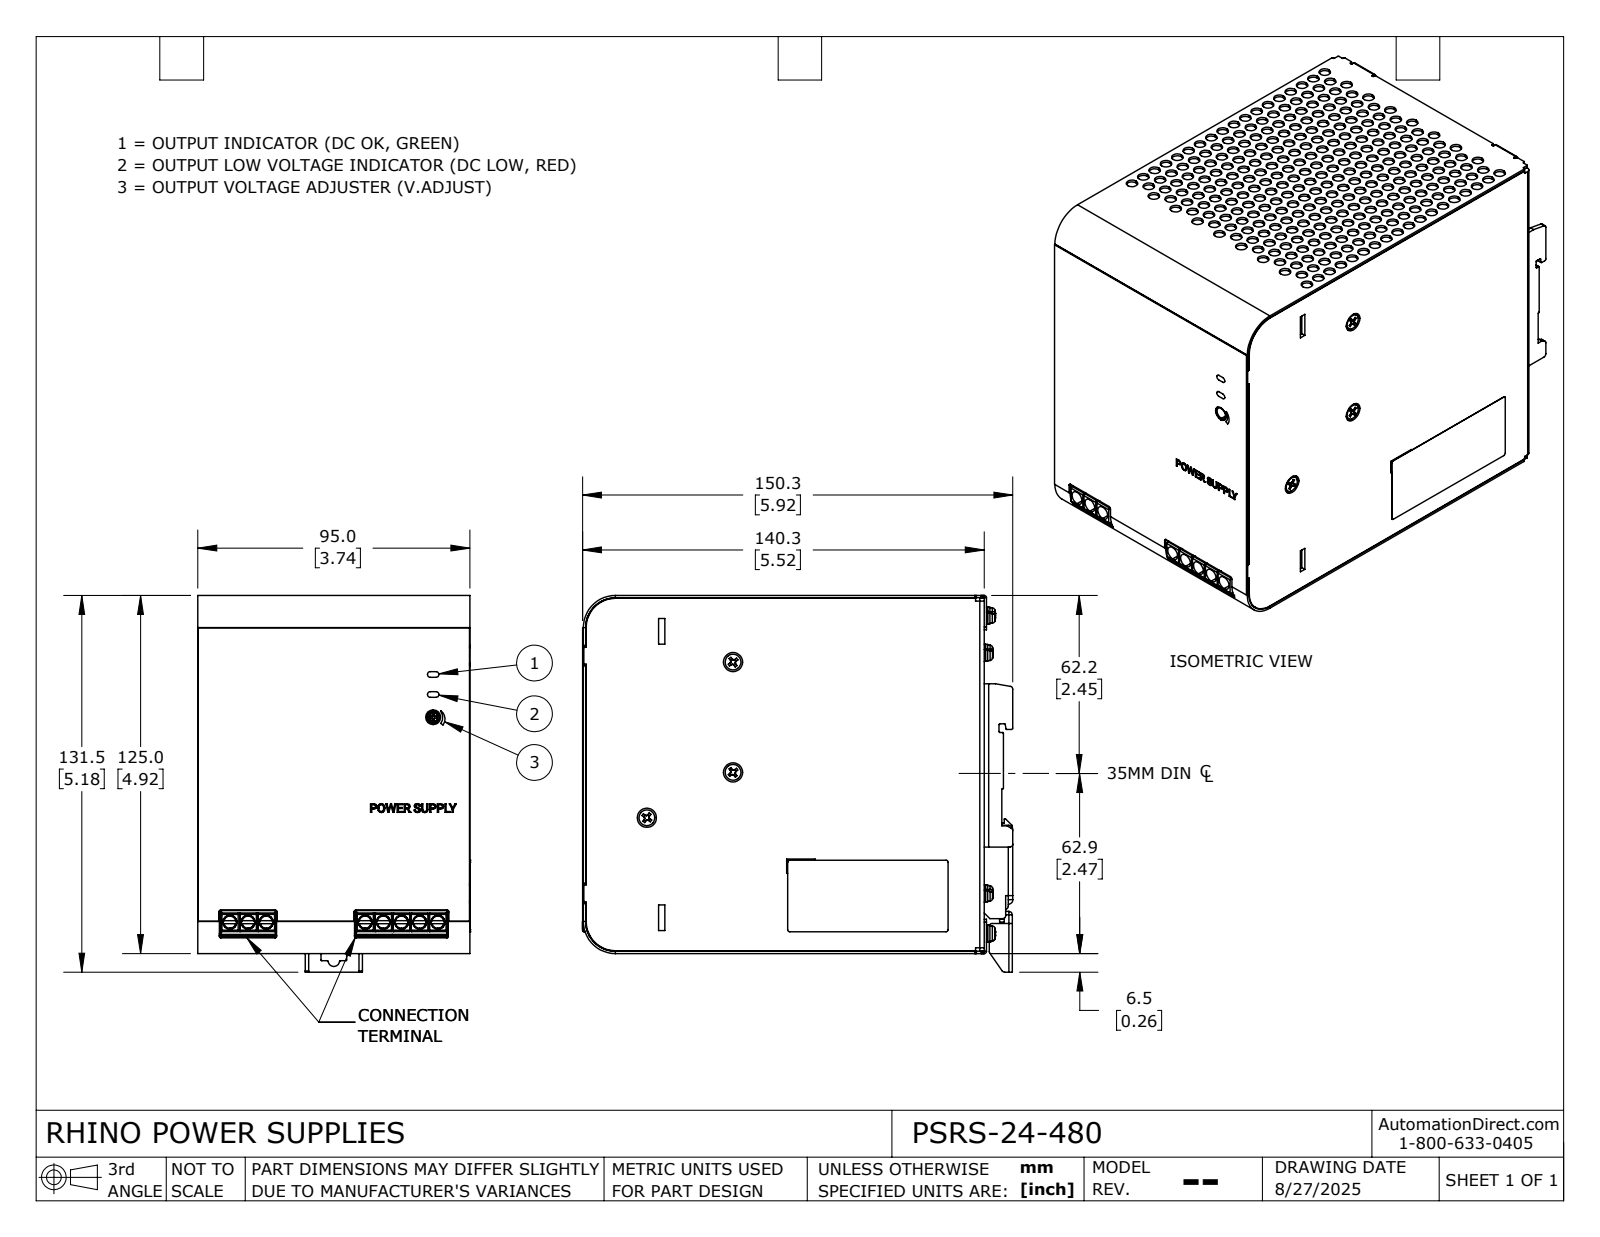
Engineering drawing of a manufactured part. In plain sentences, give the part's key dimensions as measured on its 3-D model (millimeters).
The part is named "PSRS-24-480". Its 3-D file was written by "SolidWorks 2024 (AUTOMOTIVE_DESIGN)". It is 4 solids with 4312 faces: 1983 planar, 1867 cylindrical and 462 other. Overall it measures 150.25 by 131.5 by 95.05 millimeters. Its volume is 1 662 000 cubic millimeters and its surface area 127 300 square millimeters. Round holes: 304 of diameter 4, 16 of diameter 3.1, 16 of diameter 3.5, 13 of diameter 3.6, 8 of diameter 2.5, 8 of diameter 3, 8 of diameter 3.8, 8 of diameter 4.65, 8 of diameter 4.85, 4 of diameter 6.7, 1 of diameter 1.5, 1 of diameter 3.4. Round bosses or shafts: 22 of diameter 3, 16 of diameter 6, 16 of diameter 5.9, 8 of diameter 4.75, 8 of diameter 2.96, 4 of diameter 5.5. Partial cylindrical surfaces (rounded edges, fillets, slot ends): 61 of radius 0.3, 29 of radius 0.5, 28 of radius 1, 18 of radius 0.15, 17 of radius 1.6, 13 of radius 1.2, 9 of radius 0.1, 2 of radius 0.6. The main face-to-face distances are 95, 140.25, 0.8, 124.2, 125, 1.6, 123.4, 141.85, 8.4, 10. The hole center spacings are 5.6, 12.17, 22.31, 10.8, 11.2, 21.6, 32.88, 15.56.
